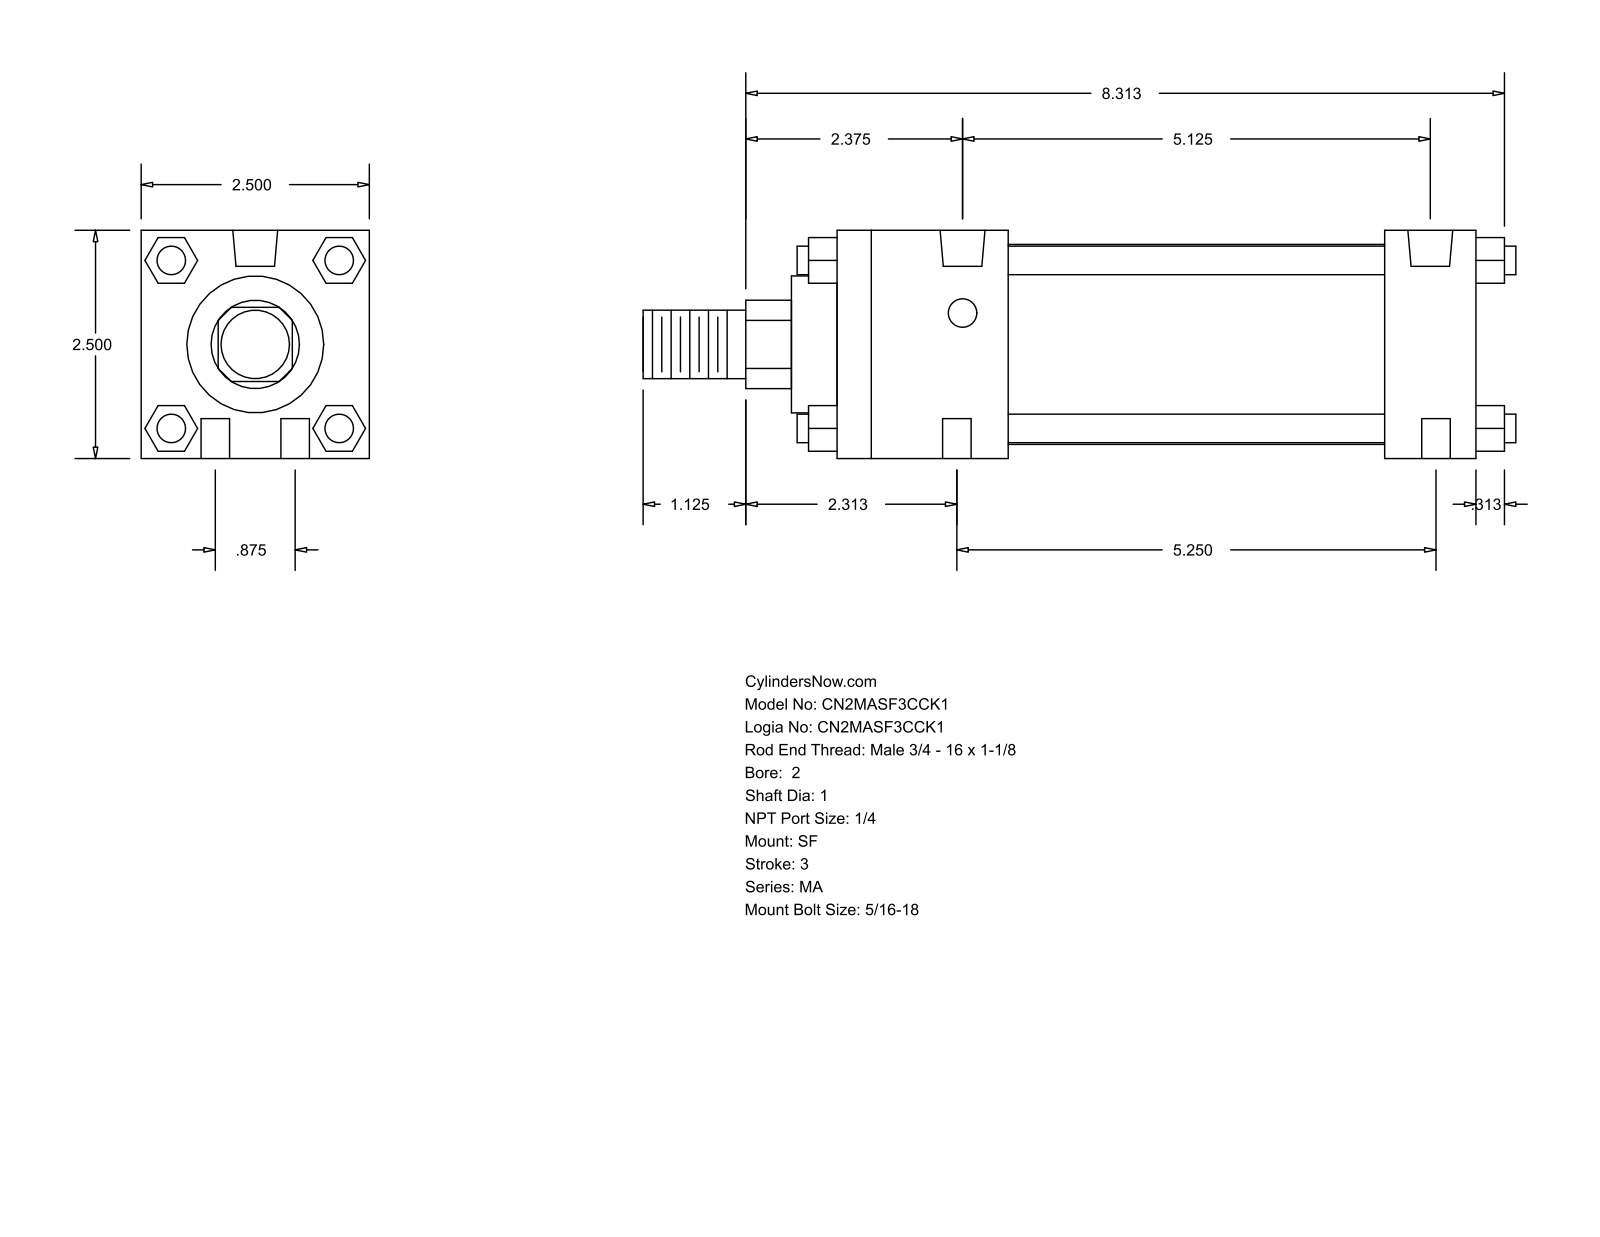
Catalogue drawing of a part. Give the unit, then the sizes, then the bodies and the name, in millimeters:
Units: millimetres
Overall size (bounding box): 242.89 × 63.5 × 63.5
Round holes (diameter × count): ⌀7.94 ×6, ⌀12.49 ×2
Round bosses / shafts (diameter × count): ⌀7.94 ×4, ⌀55.63 ×1, ⌀38.1 ×1, ⌀25.4 ×1, ⌀19.05 ×1
Partial cylindrical surfaces — rounded edges, fillets, slot ends (radius × count): R12.29 ×1
Main face-to-face distances: 63.5, 177.8, 12.7, 25.4, 152.4, 47.63, 104.77, 130.17, 40.47, 23.37
Hole centre spacings: 11.22, 132.23, 22.22, 130.17, 133.35, 135.19
Bodies: 0 solids, 124 faces (94 planar, 30 cylindrical, 0 other)
Part name (STEP PRODUCT): MA_SF__0200_1
STEP written by: GSSL Pune (CONFIG_CONTROL_DESIGN)
